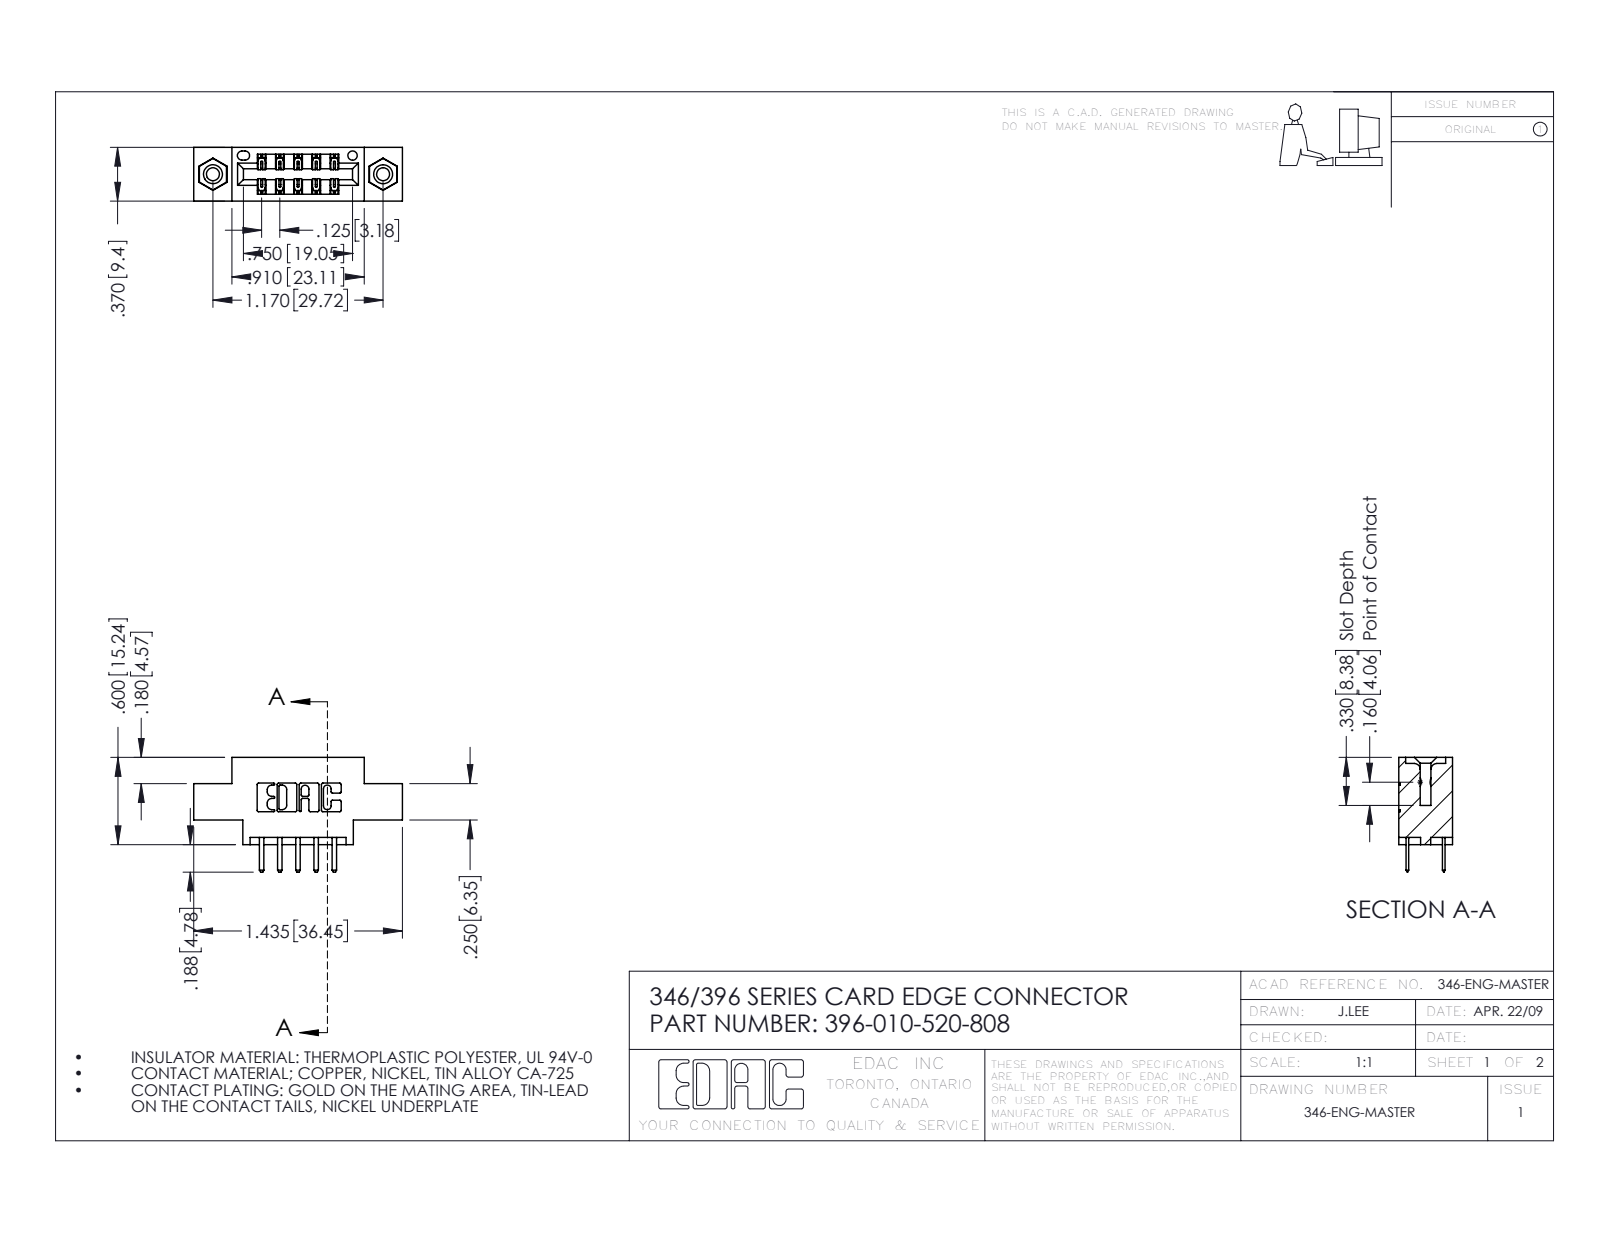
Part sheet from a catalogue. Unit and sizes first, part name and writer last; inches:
Units: inches
Overall size (bounding box): 1.435 × 0.788 × 0.37
Round holes (diameter × count): ⌀0.089 ×2, ⌀0.125 ×2, ⌀0.156 ×2, ⌀0.064 ×1
Round bosses / shafts (diameter × count): ⌀0.155 ×2
Partial cylindrical surfaces — rounded edges, fillets, slot ends (radius × count): R0.01 ×22, R0.006 ×15, R0.01 ×14, R0.007 ×6, R0.031 ×6, R0.026 ×3, R0.014 ×2, R0.022 ×2
Main face-to-face distances: 0.25, 0.37, 0.048, 0.322, 0.222, 0.148, 0.1, 0.174, 0.55, 0.072
Hole centre spacings: 0.246, 0.969, 1.17
Volume: 0.189 in³ · Surface area: 6 in²
Bodies: 13 solids, 746 faces (482 planar, 248 cylindrical, 16 other)
Part name (STEP PRODUCT): 396-010-520-808; 346 Part_0.170 Offset - 0.156 Dia-TI; 345-250-001_345-250-003-102; 345-292-001_345-293-120
STEP written by: SolidWorks 2016 (CONFIG_CONTROL_DESIGN)
